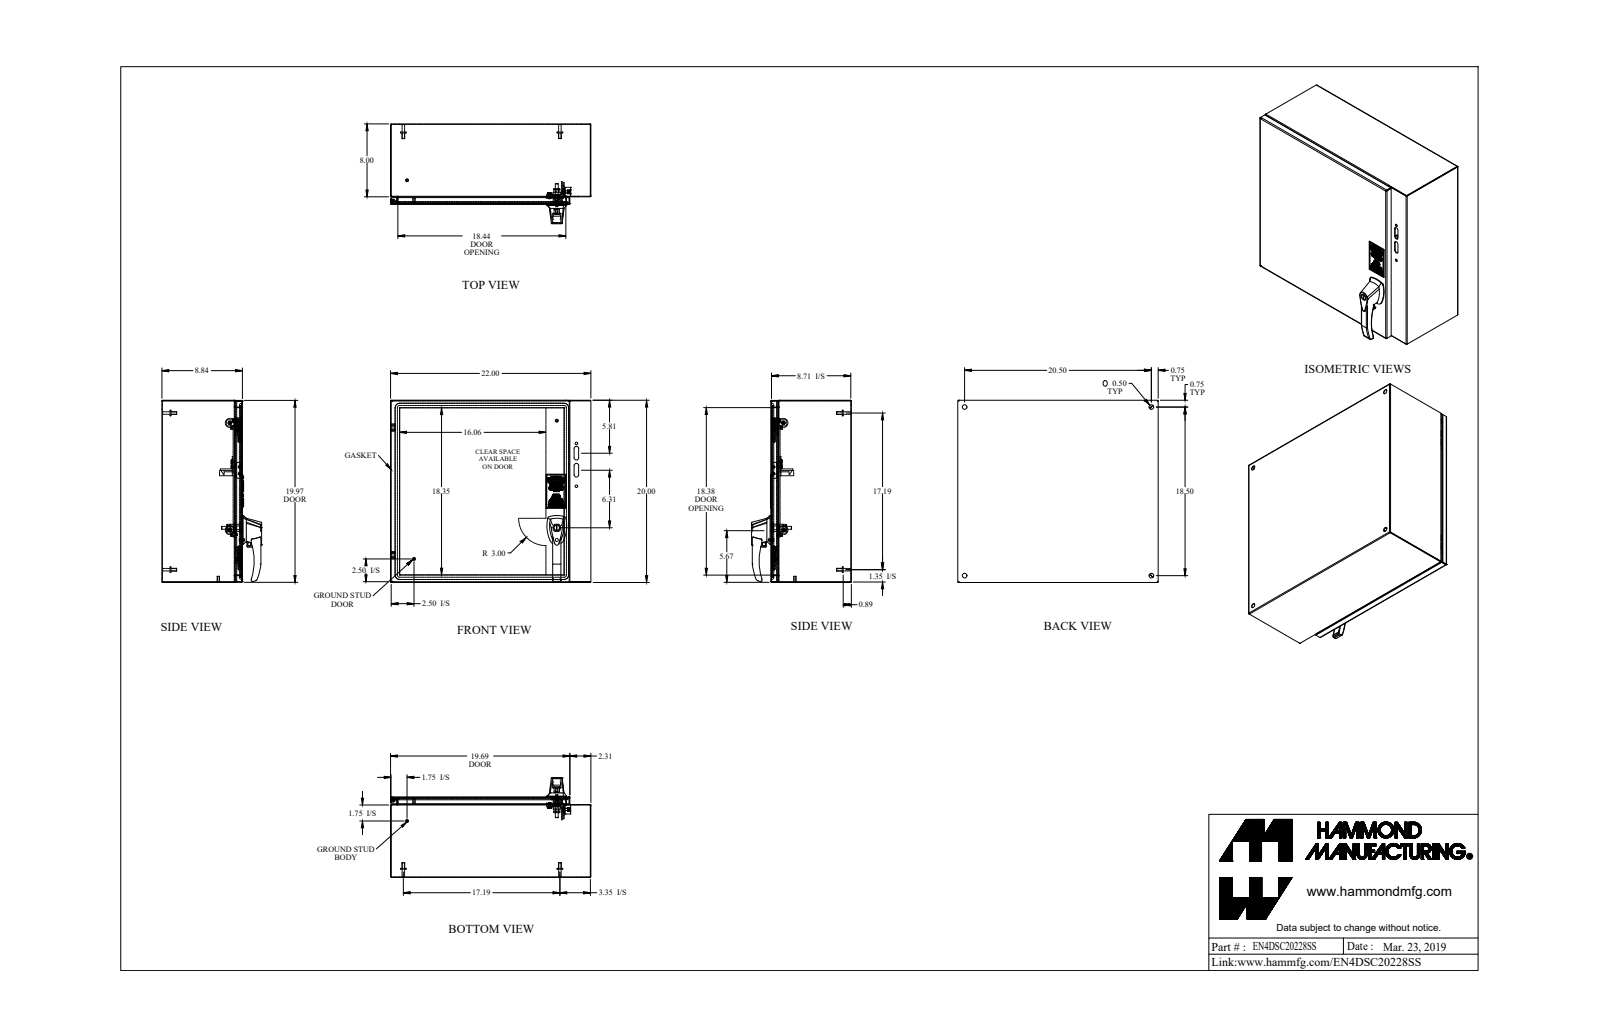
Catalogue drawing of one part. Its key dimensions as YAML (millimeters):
part_name: "EN4DSC20228SS"
step_written_by: "SolidWorks 2019 (AUTOMOTIVE_DESIGN)"
units: millimeters
bodies: {solids: 45, faces: 933, planar: 502, cylindrical: 284, other: 147}
overall_size: [558.72, 508.41, 278.18]
volume: 2376000
surface_area: 2394000
round_holes:
  - {diameter: 4.47, count: 4}
  - {diameter: 3.97, count: 2}
  - {diameter: 4.39, count: 2}
  - {diameter: 5.46, count: 2}
  - {diameter: 6.35, count: 2}
  - {diameter: 6.73, count: 2}
  - {diameter: 7.14, count: 2}
  - {diameter: 10.49, count: 2}
  - {diameter: 4.37, count: 1}
  - {diameter: 4.98, count: 1}
  - {diameter: 5.92, count: 1}
  - {diameter: 6.1, count: 1}
round_bosses_or_shafts:
  - {diameter: 6.35, count: 7}
  - {diameter: 7.94, count: 6}
  - {diameter: 9.53, count: 4}
  - {diameter: 6.99, count: 4}
  - {diameter: 3.97, count: 4}
  - {diameter: 25.4, count: 2}
  - {diameter: 15.88, count: 2}
  - {diameter: 15.87, count: 2}
partial_cylinders:
  - {radius: 2, count: 28}
  - {radius: 0.17, count: 16}
  - {radius: 6.35, count: 14}
  - {radius: 3.17, count: 11}
  - {radius: 3.83, count: 8}
  - {radius: 1.52, count: 7}
  - {radius: 0.76, count: 6}
  - {radius: 2.29, count: 6}
face_to_face_distances: [1.83, 222.63, 220.8, 224.46, 506.17, 556.67, 21.26, 508, 504.34, 201.37]
hole_center_spacings: [25.51, 28.2, 189.85, 298.45, 13.21, 19.05, 20.75, 25.2]
